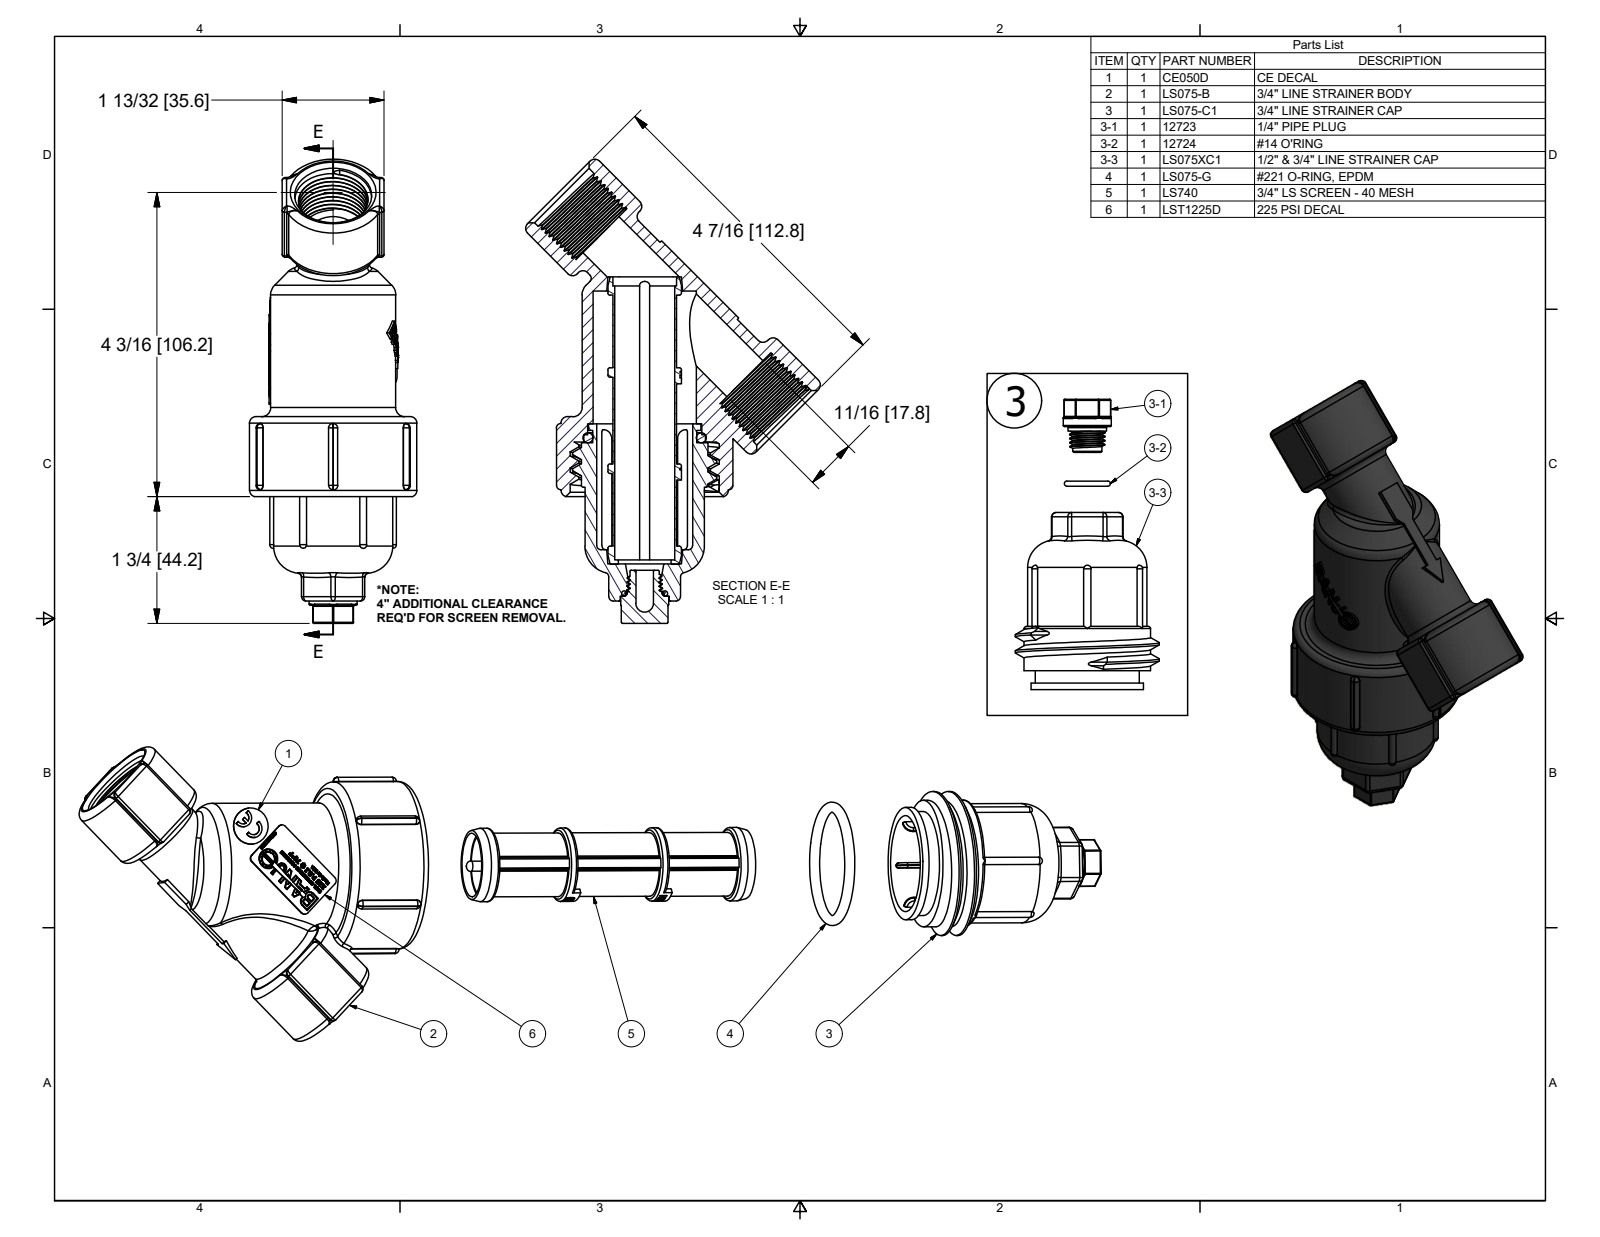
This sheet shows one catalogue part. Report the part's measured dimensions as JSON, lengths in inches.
{"part_name": "LS075-40; CE050D; LS075-B; LS075-C1 (+6 more)", "step_written_by": "Autodesk Inventor 2018 (AUTOMOTIVE_DESIGN)", "units": "inches", "bodies": {"solids": 8, "faces": 2267, "planar": 1146, "cylindrical": 386, "other": 735}, "overall_size": [21.064, 21.064, 2.3], "volume_in3": 17.38, "surface_area_in2": 584.5, "round_holes": [[0.181, 2], [0.257, 2], [0.24, 1], [0.675, 1], [0.7, 1], [0.725, 1], [0.825, 1], [1.32, 1], [1.42, 1], [1.57, 1], [1.671, 1], [1.809, 1]], "round_bosses_or_shafts": [[0.27, 2], [2.3, 1], [1.981, 1], [1.74, 1], [1.72, 1], [1.64, 1], [1.545, 1], [1.43, 1]], "partial_cylinders_radius": [[0.06, 67], [0.03, 35], [0.015, 26], [0.125, 8], [0.05, 6], [0.026, 4], [0.033, 4], [0.063, 4]], "face_to_face_distances": [0.25, 1.4, 0.16, 1.56, 3.75, 0.07, 0.26, 2.085, 2.075, 1.825], "hole_center_spacings": [0.638]}
